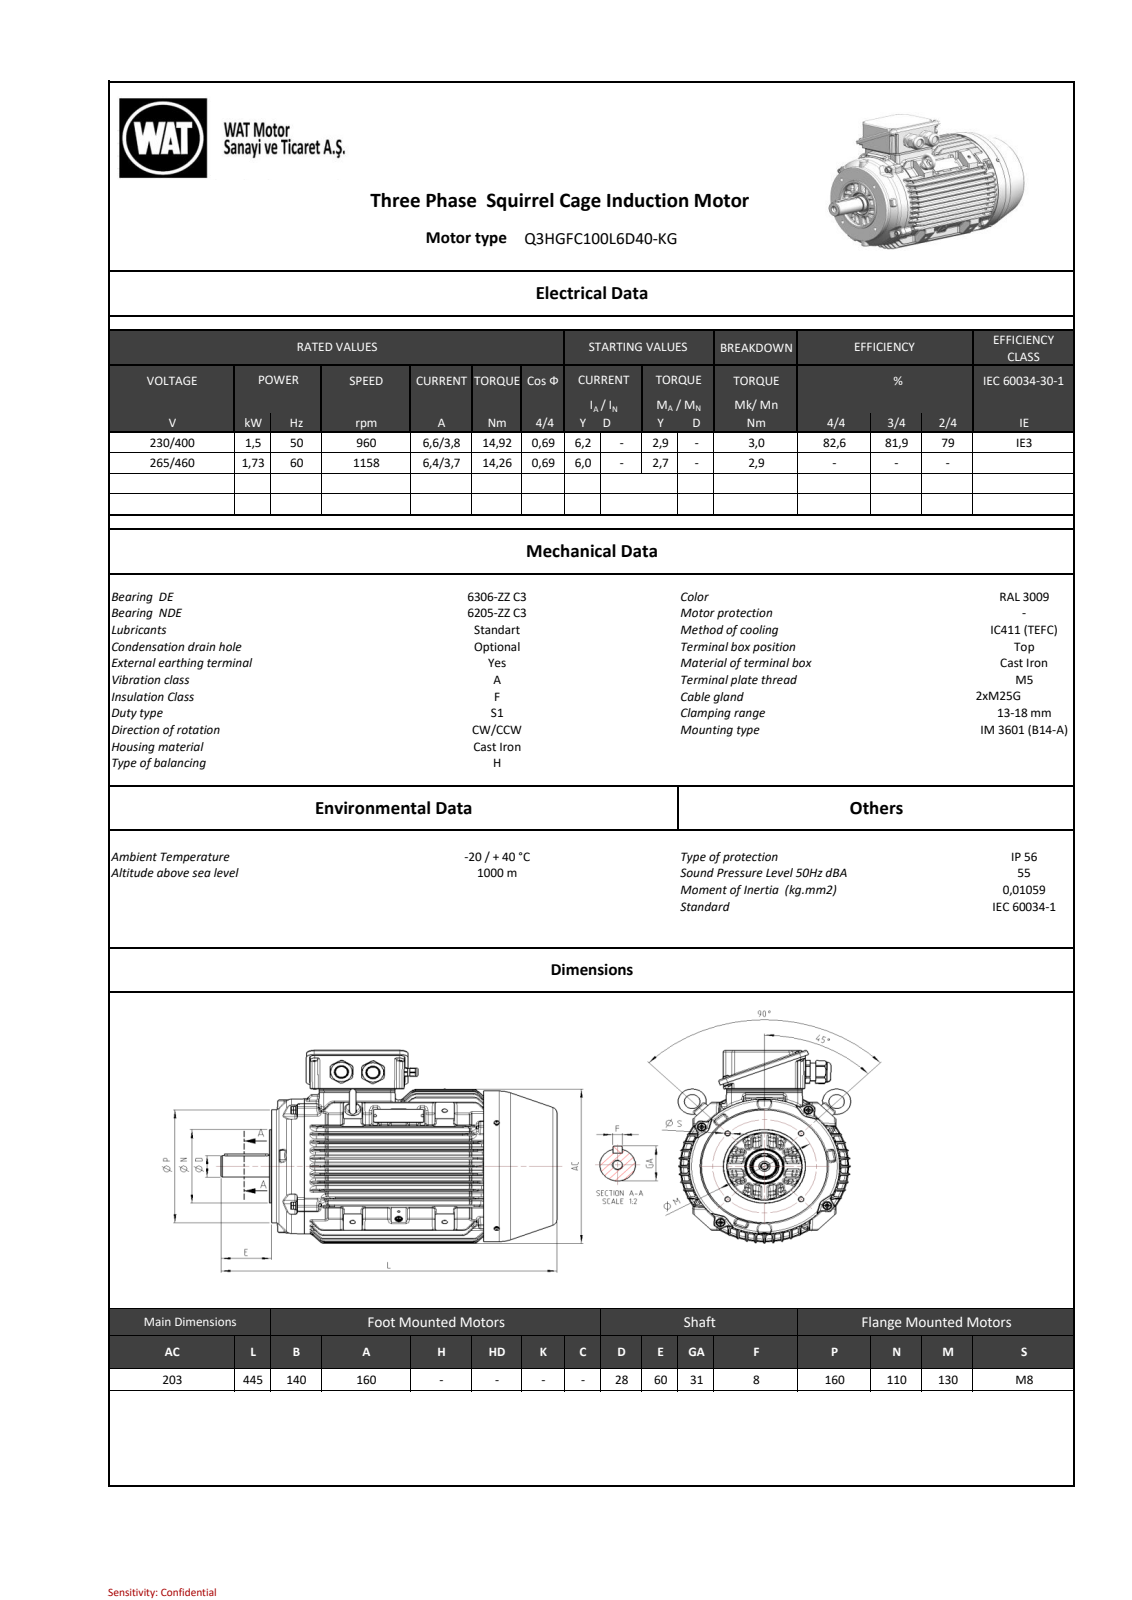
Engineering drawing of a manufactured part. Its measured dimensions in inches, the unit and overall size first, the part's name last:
Units: inches
Overall size (bounding box): 17.52 × 10.746 × 8.069
Round holes (diameter × count): ⌀0.268 ×10, ⌀0.197 ×8, ⌀0.394 ×5, ⌀0.165 ×2, ⌀0.677 ×2, ⌀0.256 ×1, ⌀0.335 ×1, ⌀0.413 ×1, ⌀1.709 ×1, ⌀1.717 ×1, ⌀7.756 ×1
Round bosses / shafts (diameter × count): ⌀0.472 ×6, ⌀0.394 ×4, ⌀0.341 ×4, ⌀0.315 ×4, ⌀0.157 ×4, ⌀1.091 ×2, ⌀0.994 ×2, ⌀0.787 ×2
Partial cylindrical surfaces — rounded edges, fillets, slot ends (radius × count): R0.157 ×239, R0.059 ×101, R0.118 ×85, R0.071 ×42, R0.039 ×36, R0.079 ×33, R0.01 ×24, R1.043 ×12
Main face-to-face distances: 0.533, 1.069, 0.536, 1.608, 1.075, 0.539, 3.104, 2.567, 2.035, 2.15
Hole centre spacings: 1.097, 3.524, 3.979, 4.7, 4.983, 6.06, 2.303, 2.815
Bodies: 0 solids, 4431 faces (861 planar, 1043 cylindrical, 2527 other)
Part name (STEP PRODUCT): 260051B46F5629wg
STEP written by: SIEMENS PLM Software NX 11.0 (AUTOMOTIVE_DESIGN)
